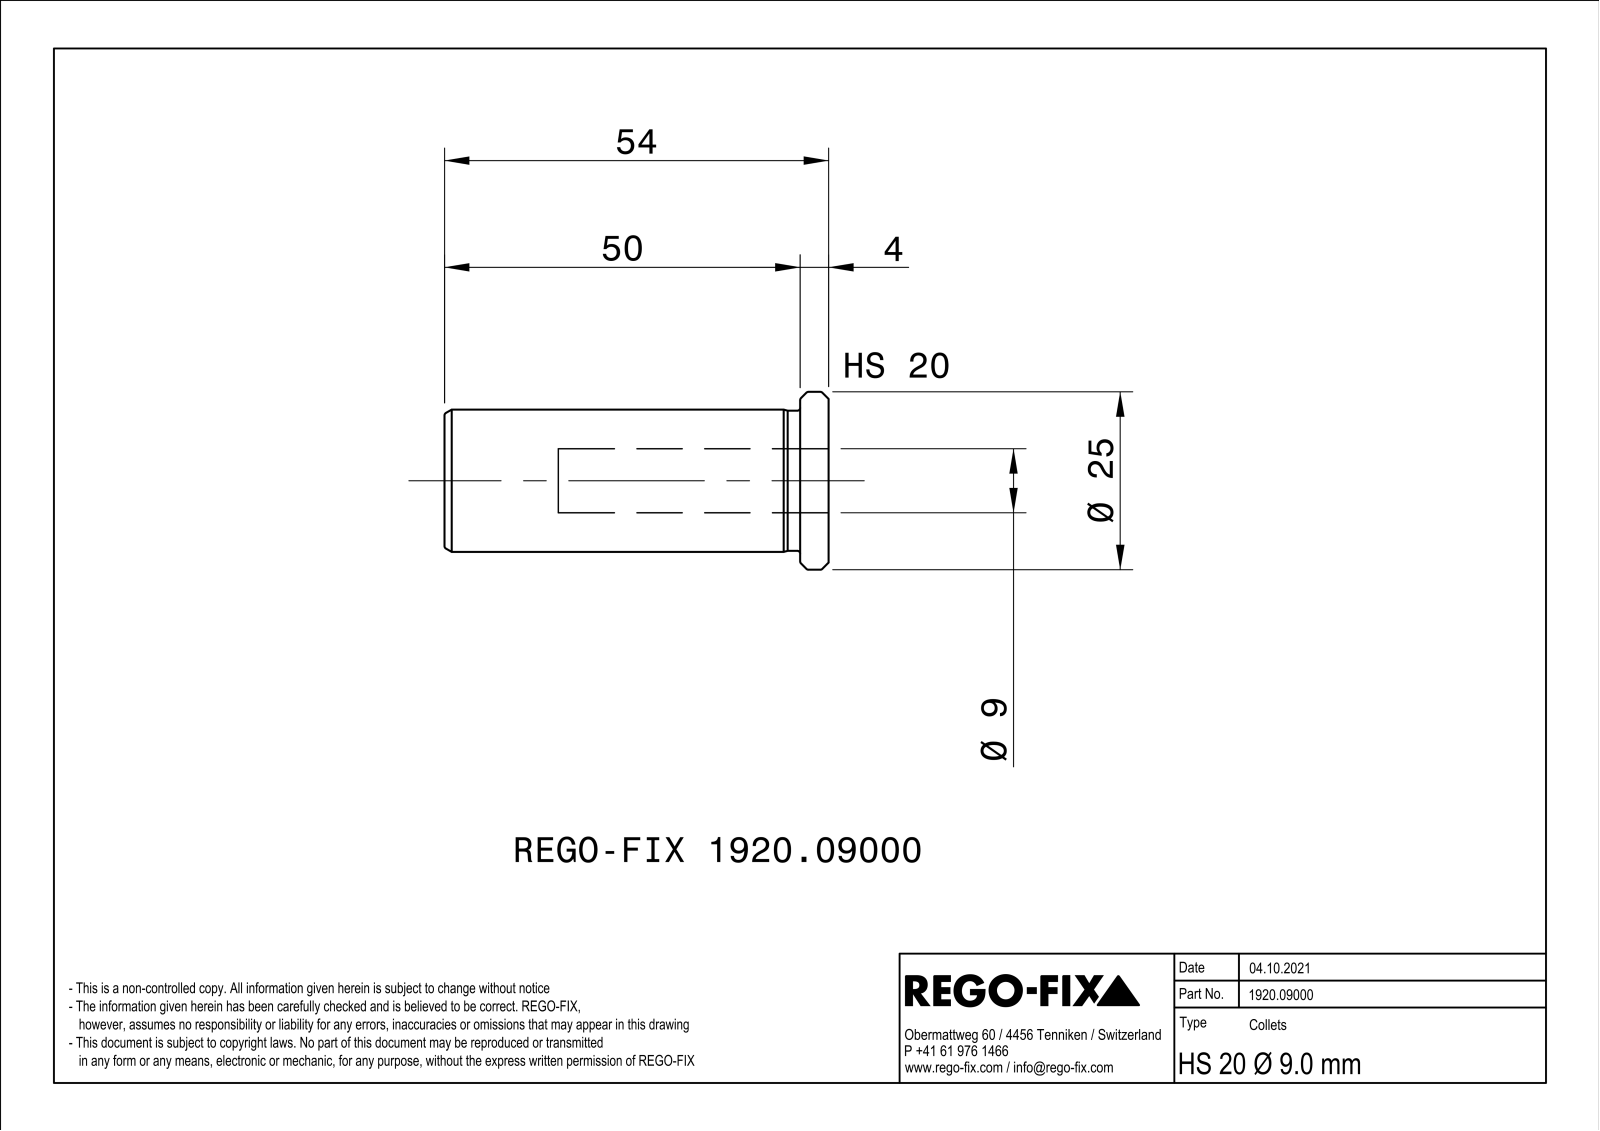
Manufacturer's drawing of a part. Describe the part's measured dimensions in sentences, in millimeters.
The part is named "NOCUT". Its 3-D file was written by "SIEMENS PLM Software Solid Edge ST10 (AUTOMOTIVE_DESIGN)". It is 1 solid with 73 faces: 22 planar, 12 cylindrical and 39 other. Overall it measures 54 by 24.99 by 24.99 millimeters. Its volume is 11 635 cubic millimeters and its surface area 7 351 square millimeters. Round holes: 1 of diameter 9, 1 of diameter 10.5, 1 of diameter 16.5. Round bosses or shafts: 1 of diameter 25, 1 of diameter 20, 1 of diameter 19.7. The main face-to-face distances are 0.8, 4, 54, 50.
